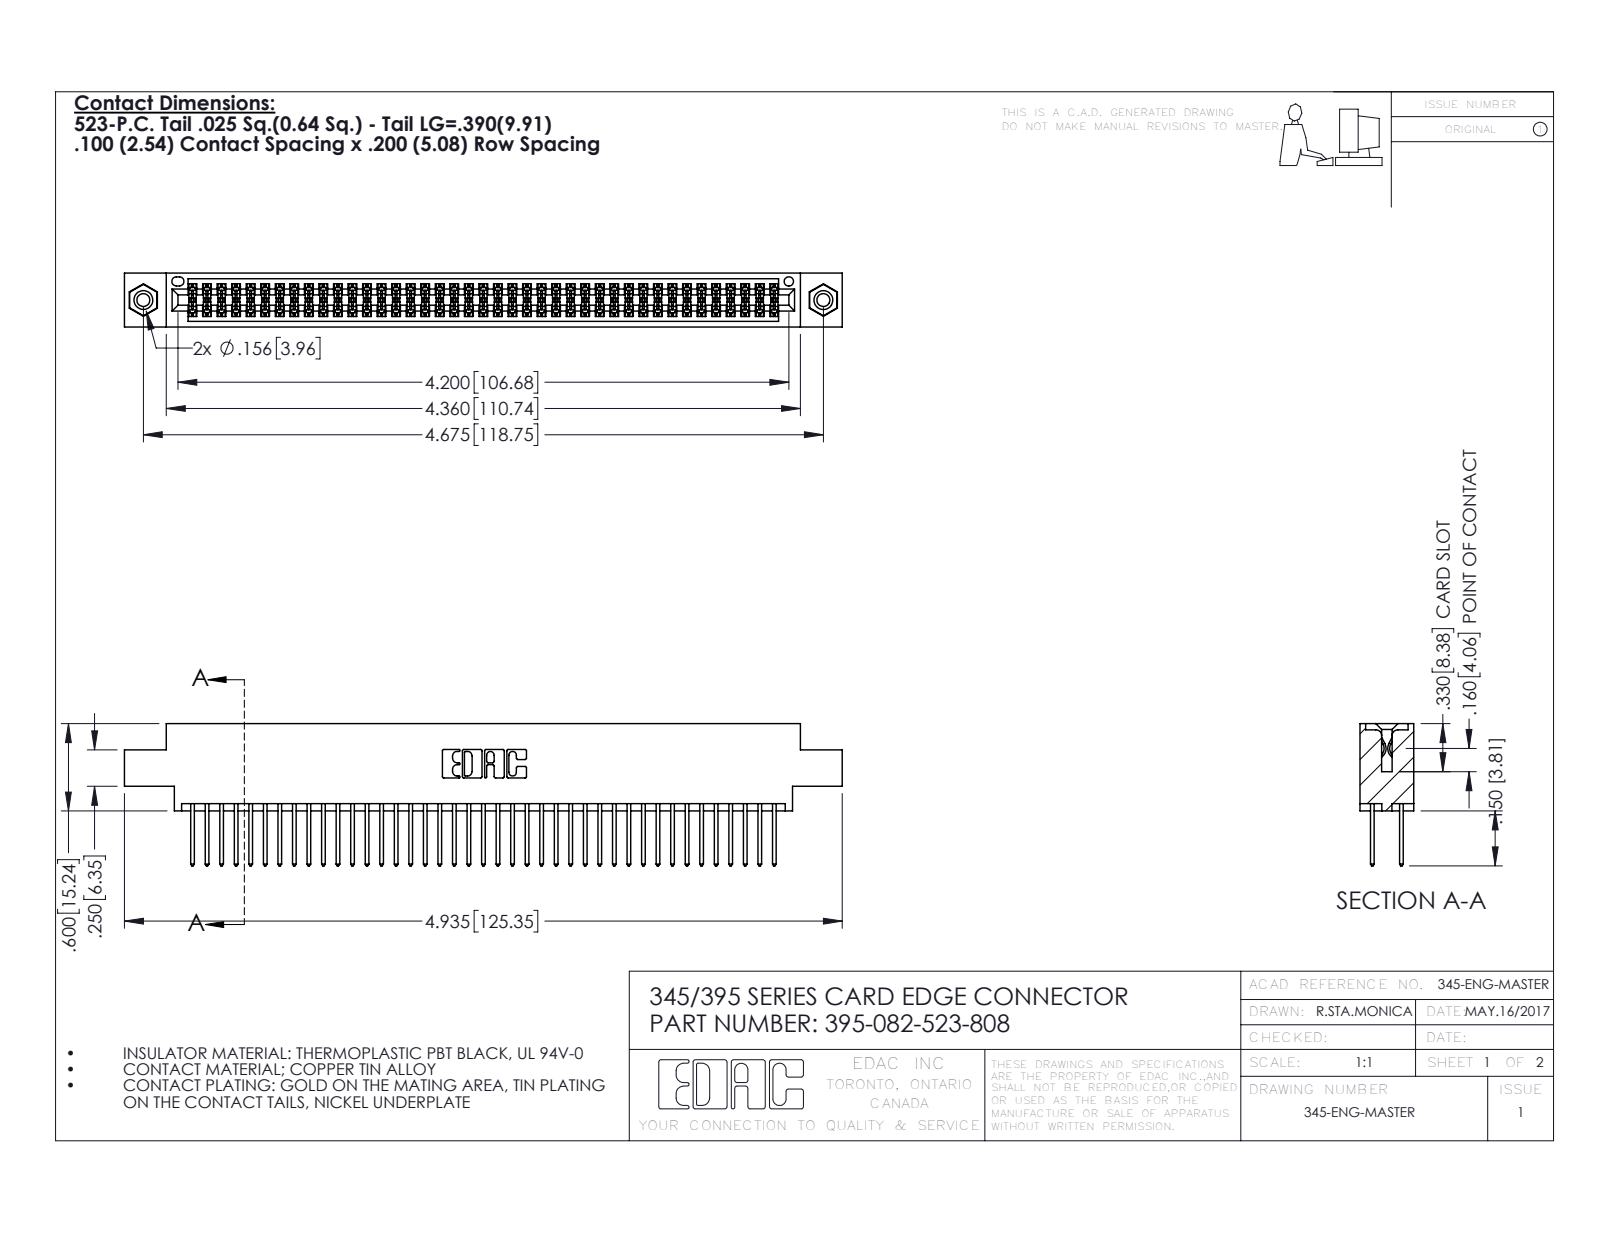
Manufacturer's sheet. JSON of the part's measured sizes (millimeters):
{"part_name": "345-250-001_345-250-003-102; 345-292-001_345-293-123; 345 Part_0.170 Offset - 0.156 Dia-TI; 395-082-523-808", "step_written_by": "SolidWorks 2016 (CONFIG_CONTROL_DESIGN)", "units": "millimeters", "bodies": {"solids": 85, "faces": 4290, "planar": 2822, "cylindrical": 1452, "other": 16}, "overall_size": [125.3, 24.8, 9.4], "volume_mm3": 12200, "surface_area_mm2": 18950, "round_holes": [[2.3, 2], [3.2, 2], [4, 2], [1.6, 1]], "round_bosses_or_shafts": [[3.9, 2]], "partial_cylinders_radius": [[0.2, 123], [0.3, 82], [0.3, 22], [0.2, 6], [0.8, 6], [0.7, 3], [0.4, 2], [0.5, 2]], "face_to_face_distances": [1.8, 7.6, 5.1, 2.5, 6.9, 0.6, 9.4, 5.7, 4.4, 3.8], "hole_center_spacings": [6.9, 112.8, 118.7]}
